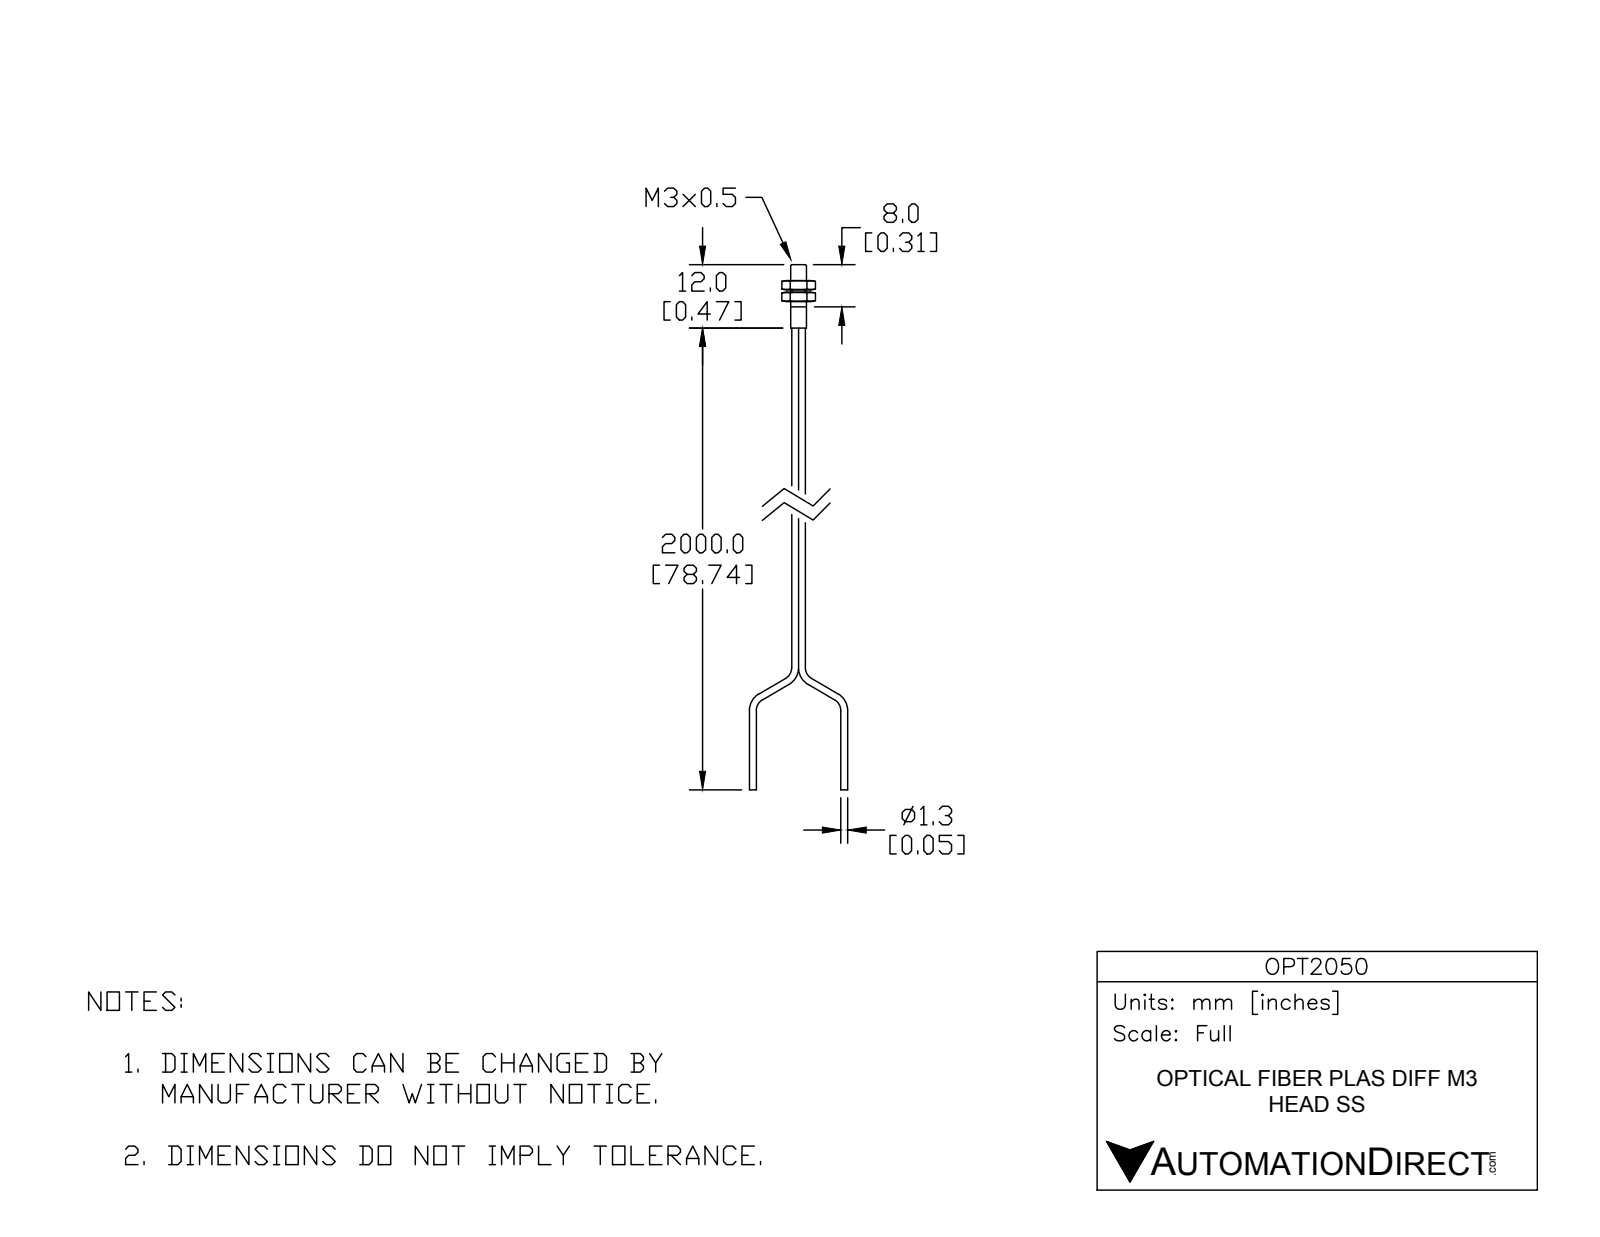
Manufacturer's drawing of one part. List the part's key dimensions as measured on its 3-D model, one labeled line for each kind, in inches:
Part name (STEP PRODUCT): OPT2050
STEP written by: SolidWorks 2014 (AUTOMOTIVE_DESIGN)
Units: inches
Bodies: 5 solids, 75 faces (27 planar, 26 cylindrical, 22 other)
Overall size (bounding box): 3.666 × 0.707 × 0.217
Volume: 0.015 in³ · Surface area: 1.143 in²
Round holes (diameter × count): ⌀0.043 ×1, ⌀0.085 ×1
Round bosses / shafts (diameter × count): ⌀0.039 ×6, ⌀0.118 ×1
Main face-to-face distances: 0.217, 0.071, 0.087, 0.157, 0.016, 0.228, 0.244, 0.315, 0.079, 0.472
